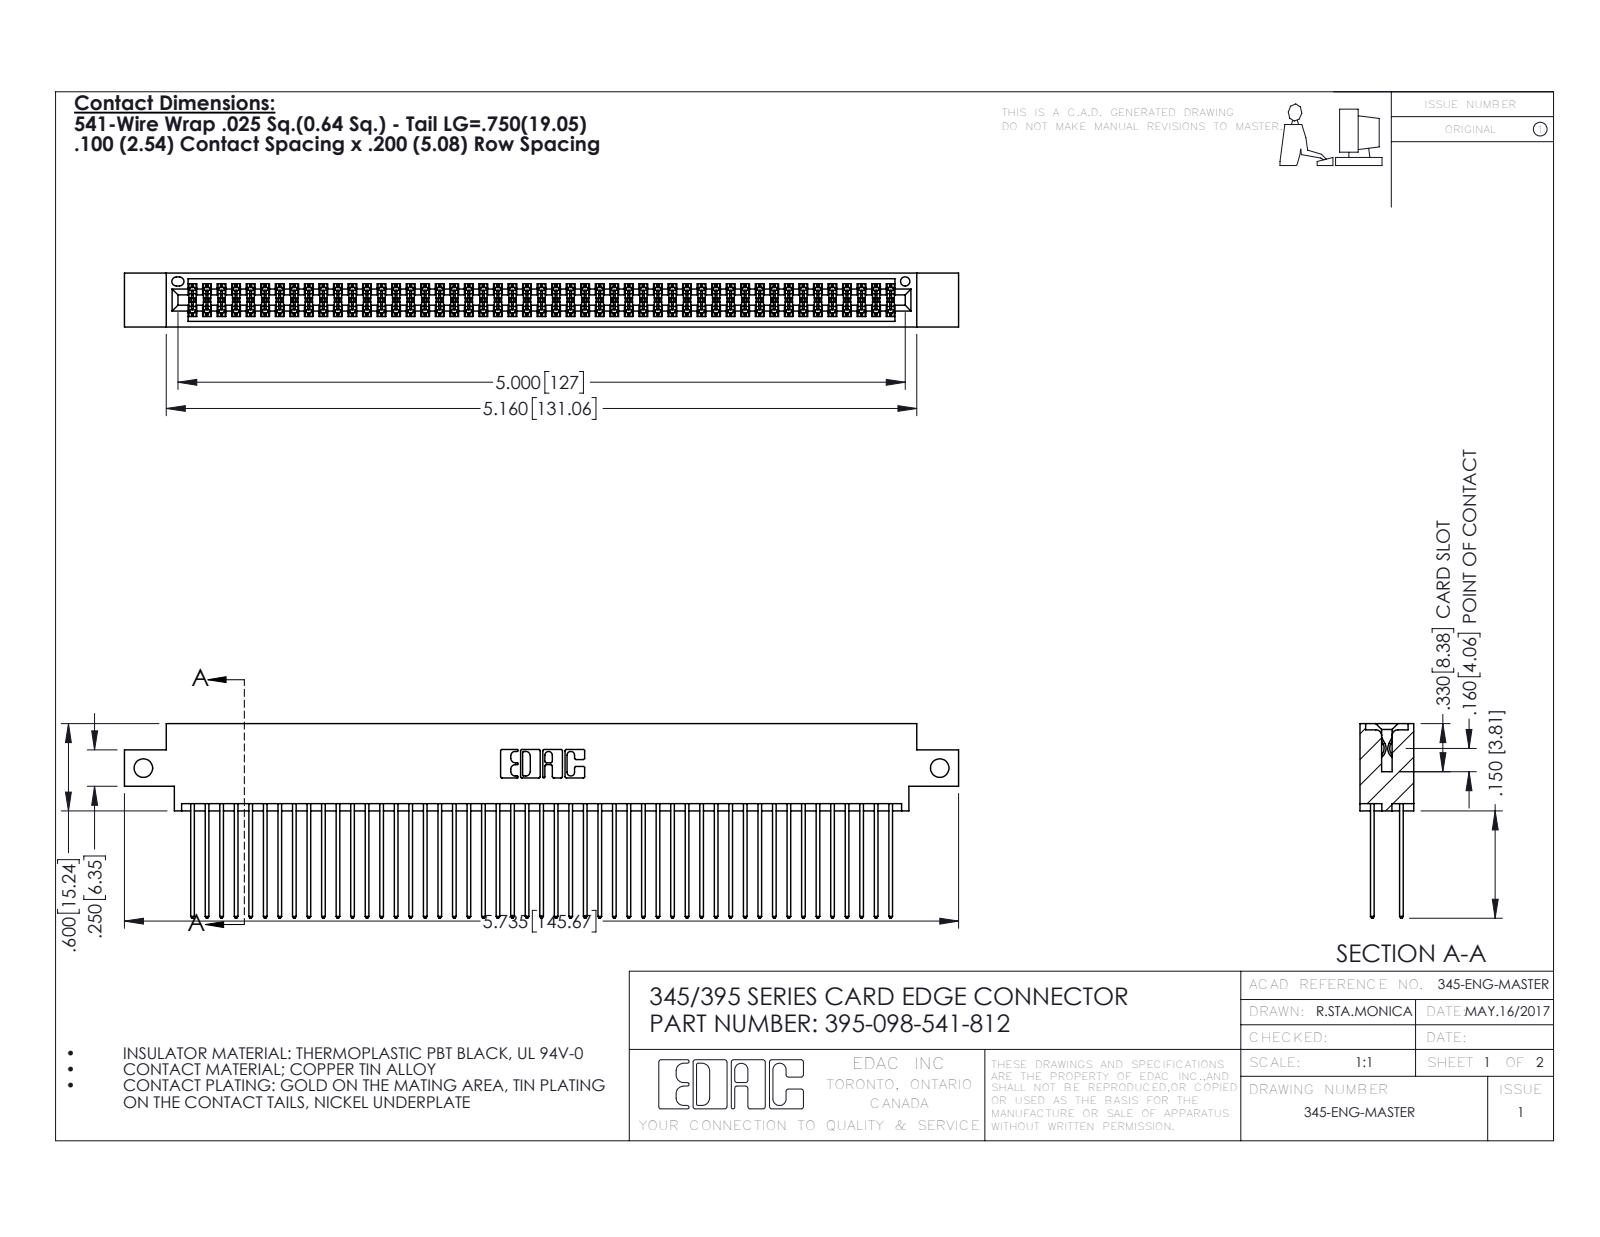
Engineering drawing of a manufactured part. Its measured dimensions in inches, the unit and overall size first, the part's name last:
Units: inches
Overall size (bounding box): 5.735 × 1.337 × 0.37
Round holes (diameter × count): ⌀0.128 ×2, ⌀0.064 ×1
Partial cylindrical surfaces — rounded edges, fillets, slot ends (radius × count): R0.006 ×147, R0.01 ×98, R0.01 ×22, R0.007 ×6, R0.031 ×6, R0.026 ×3, R0.014 ×2, R0.019 ×2
Main face-to-face distances: 0.298, 0.072, 0.2, 0.098, 0.272, 0.025, 0.225, 0.37, 0.175, 0.149
Hole centre spacings: 5.475
Volume: 0.89 in³ · Surface area: 37.72 in²
Bodies: 99 solids, 5030 faces (3318 planar, 1712 cylindrical, 0 other)
Part name (STEP PRODUCT): 395-098-541-812; 345-292-001_345-293-141; 345 Part_0.170 Offset - Side Mount
STEP written by: SolidWorks 2016 (CONFIG_CONTROL_DESIGN)
